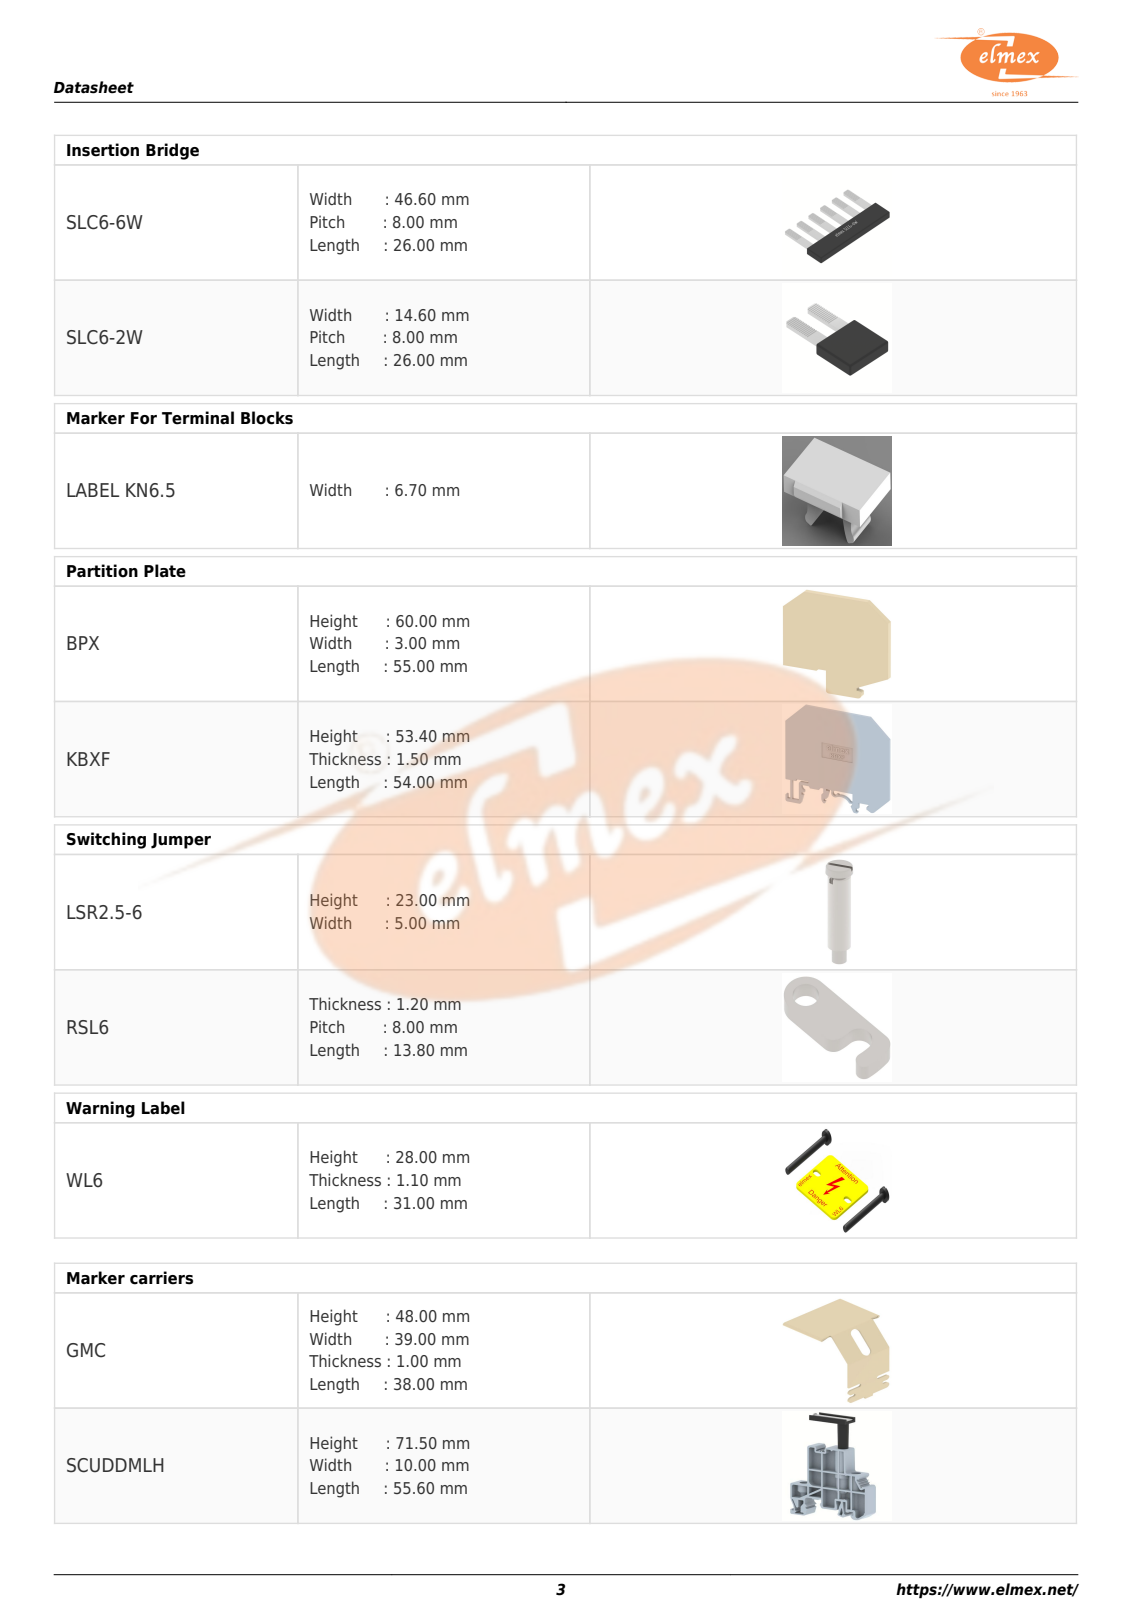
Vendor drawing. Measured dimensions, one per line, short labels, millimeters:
written by: ST-DEVELOPER v16 (AUTOMOTIVE_DESIGN)
unit: mm
bodies: 1 solid, 38 faces (33 planar, 5 cylindrical, 0 other)
size: 61.25 × 50 × 8
volume: 20 438 mm³; area: 6 955 mm²
rounds: 1× R0.12, 1× R1.25, 1× R1.88, 1× R2.06, 1× R2.5
face distances: 8, 50, 61.25, 31.25, 18.75, 15.63, 45.62, 2.63, 17, 1.37
